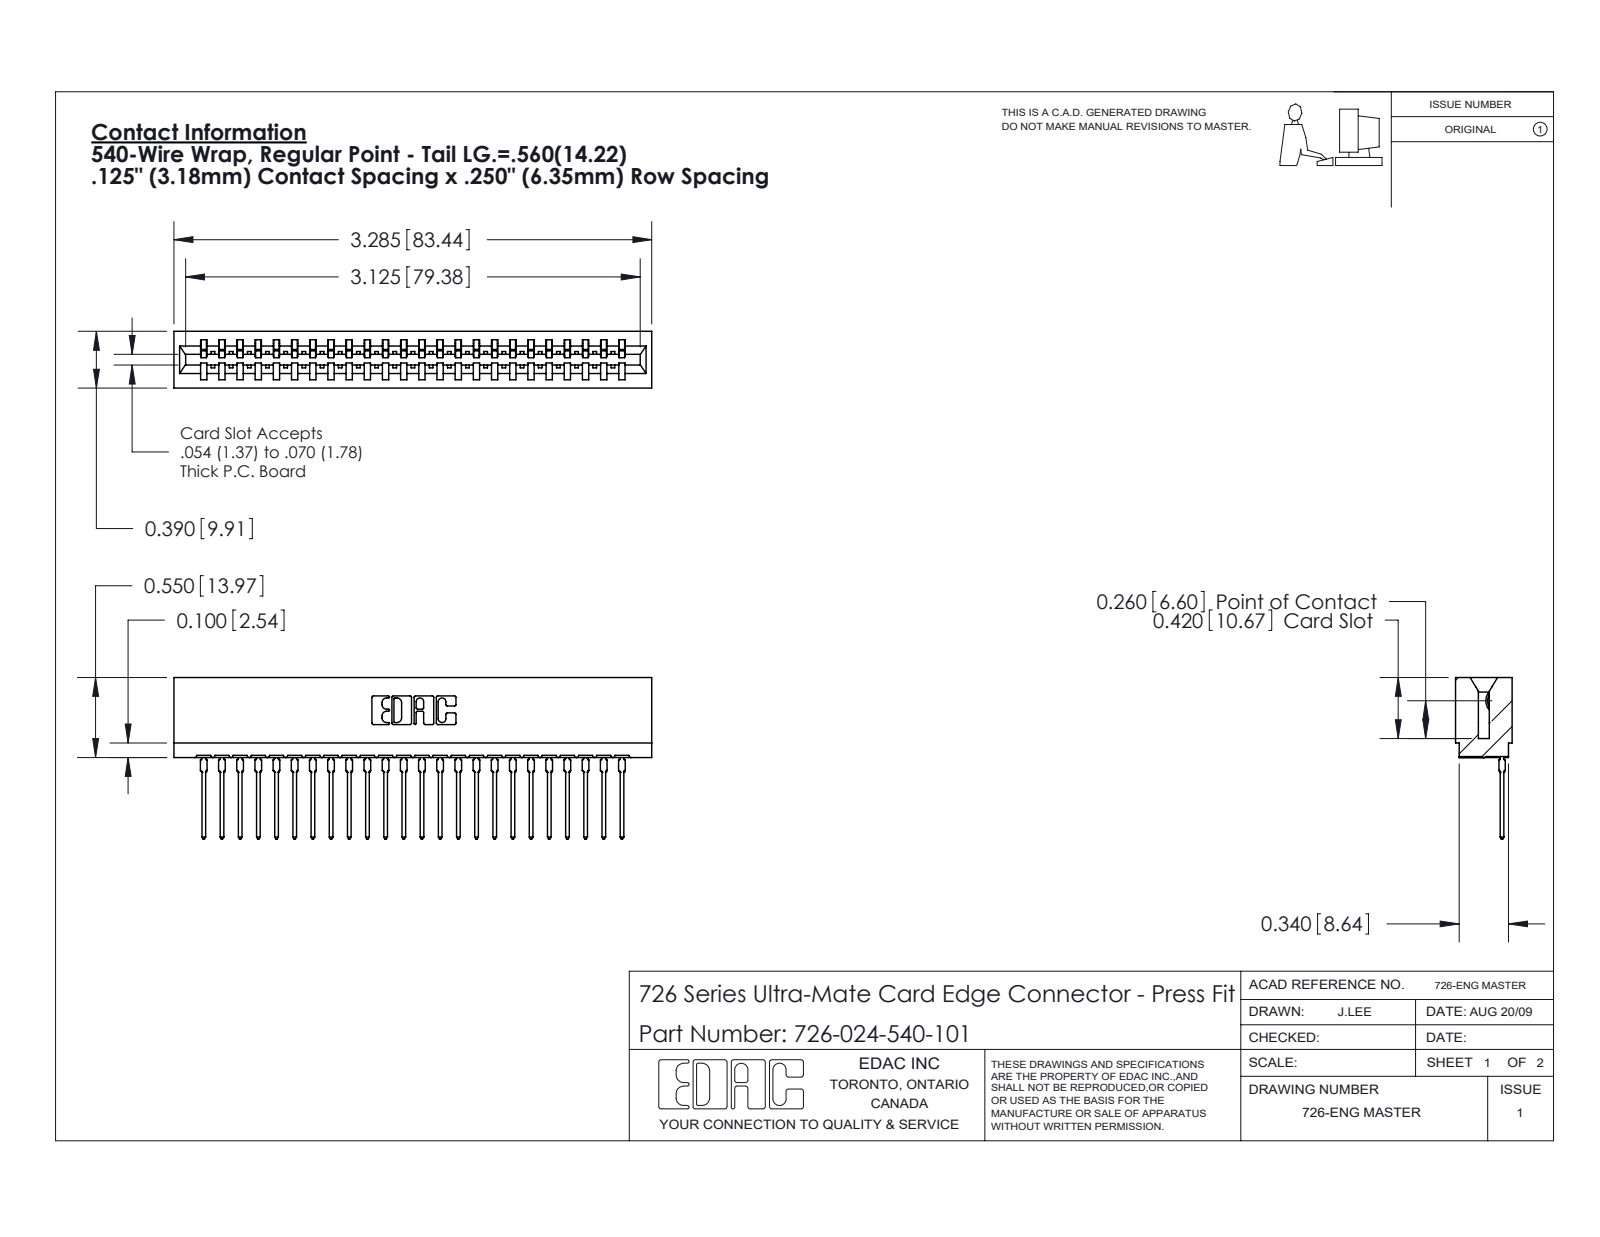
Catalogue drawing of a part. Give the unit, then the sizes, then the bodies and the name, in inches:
Units: inches
Overall size (bounding box): 3.285 × 1.109 × 0.39
Partial cylindrical surfaces — rounded edges, fillets, slot ends (radius × count): R0.021 ×48, R0.015 ×25, R0.01 ×22, R0.007 ×6, R0.031 ×6, R0.005 ×4, R0.011 ×4, R0.026 ×3
Main face-to-face distances: 0.057, 0.333, 0.39, 0.025, 0.25, 0.307, 0.083, 0.042, 0.75, 0.275
Volume: 0.464 in³ · Surface area: 18.04 in²
Bodies: 25 solids, 2689 faces (1567 planar, 498 cylindrical, 624 other)
Part name (STEP PRODUCT): 746-292-001_540; 726 Part_.515 Slot Depth - 01; 726-024-540-101
STEP written by: SolidWorks 2020 (CONFIG_CONTROL_DESIGN)
